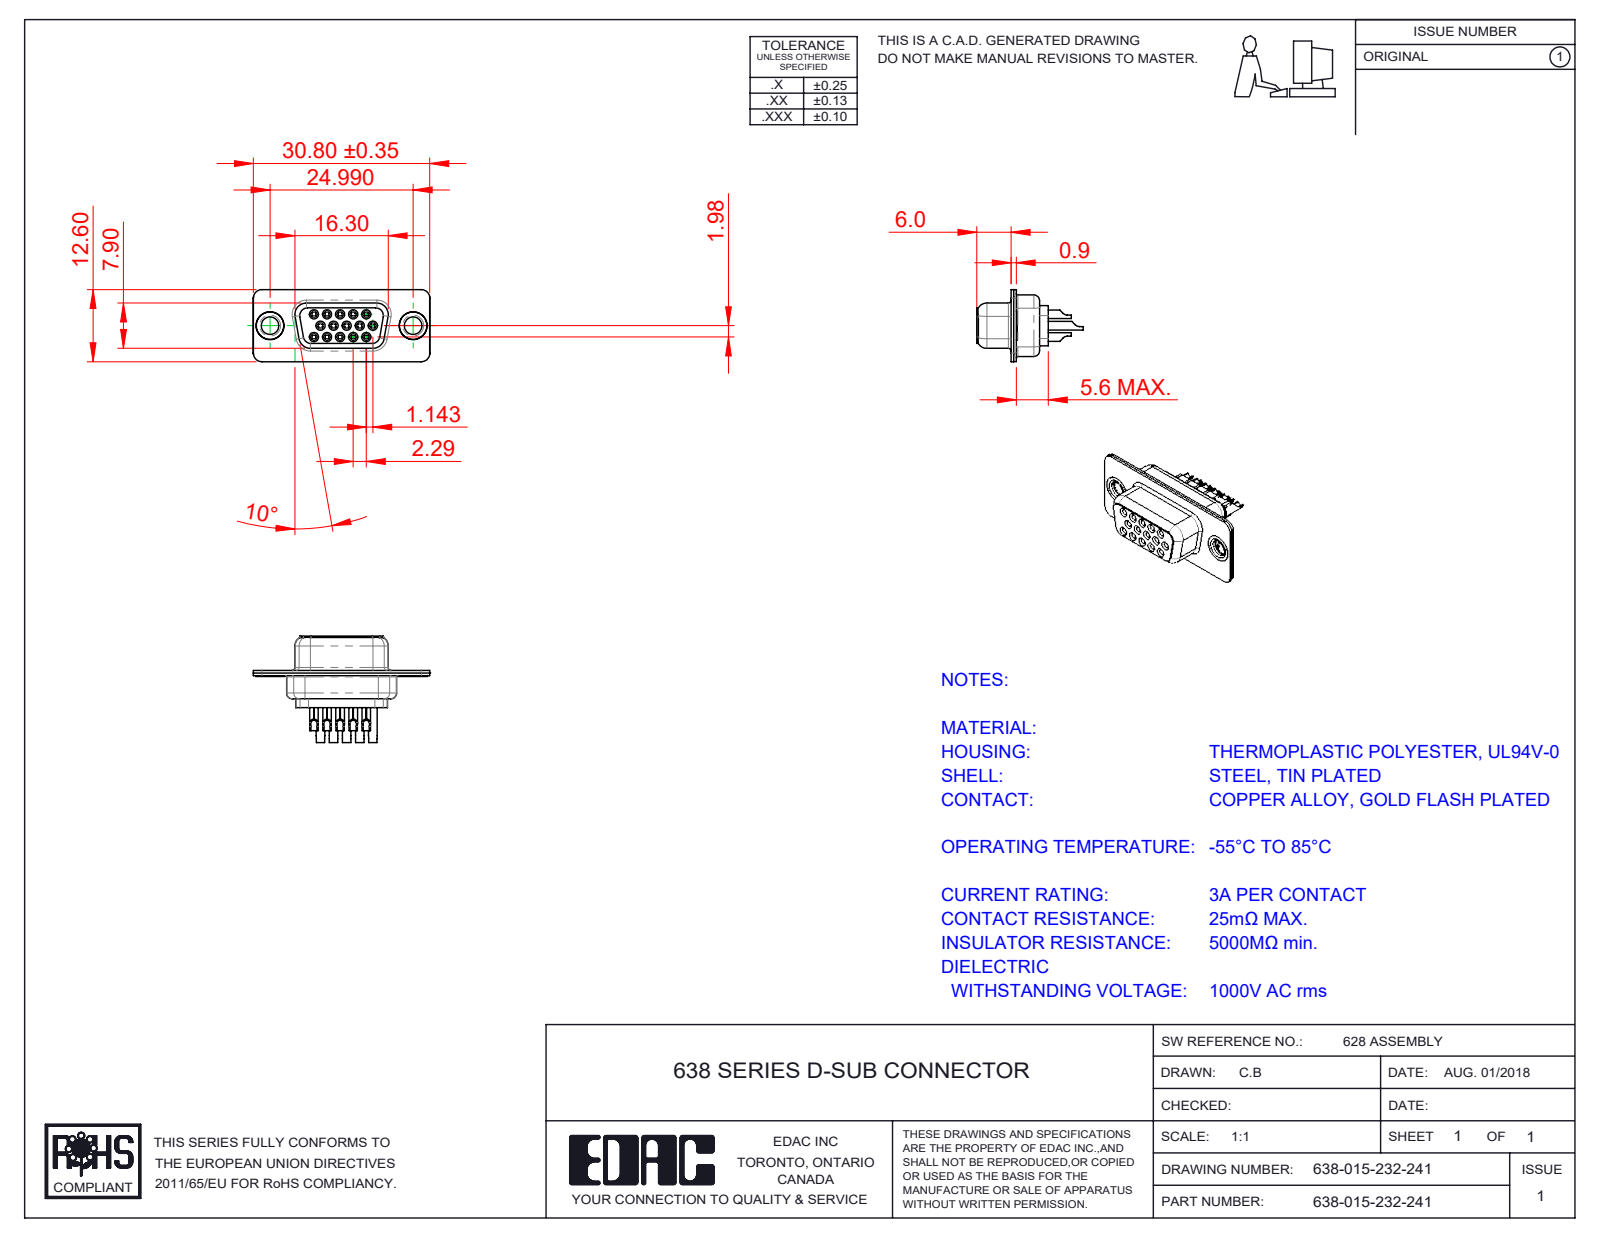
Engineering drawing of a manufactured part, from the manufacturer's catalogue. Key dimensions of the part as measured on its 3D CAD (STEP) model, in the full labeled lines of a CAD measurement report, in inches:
Part name (STEP PRODUCT): 638 Shell Rear_15 Contacts; 638 Thru Hole Rivet; 638-015-232-241; 638 Contact Row 2_32 (+4 more)
STEP written by: SolidWorks 2020 (CONFIG_CONTROL_DESIGN)
Units: inches
Bodies: 20 solids, 1588 faces (382 planar, 496 cylindrical, 710 other)
Overall size (bounding box): 1.213 × 0.732 × 0.496
Volume: 0.093 in³ · Surface area: 8.858 in²
Round holes (diameter × count): ⌀0.031 ×15, ⌀0.039 ×15, ⌀0.043 ×15, ⌀0.063 ×15, ⌀0.067 ×15, ⌀0.071 ×15, ⌀0.079 ×2, ⌀0.12 ×2, ⌀0.157 ×2, ⌀0.159 ×2, ⌀0.191 ×2
Round bosses / shafts (diameter × count): ⌀0.079 ×15, ⌀0.059 ×15, ⌀0.047 ×15, ⌀0.197 ×2, ⌀0.195 ×2, ⌀0.189 ×2, ⌀0.14 ×2
Partial cylindrical surfaces — rounded edges, fillets, slot ends (radius × count): R0.059 ×20, R0.079 ×12, R0.011 ×10, R0.061 ×8, R0.039 ×7, R0.053 ×5, R0.01 ×4, R0.02 ×4
Main face-to-face distances: 0.018, 0.035, 0.016, 0.056, 0.35, 0.26, 0.055, 0.09, 0.278, 0.033
Hole centre spacings: 0.156, 0.09, 0.18, 0.09, 0.238, 0.238, 0.27, 0.312
